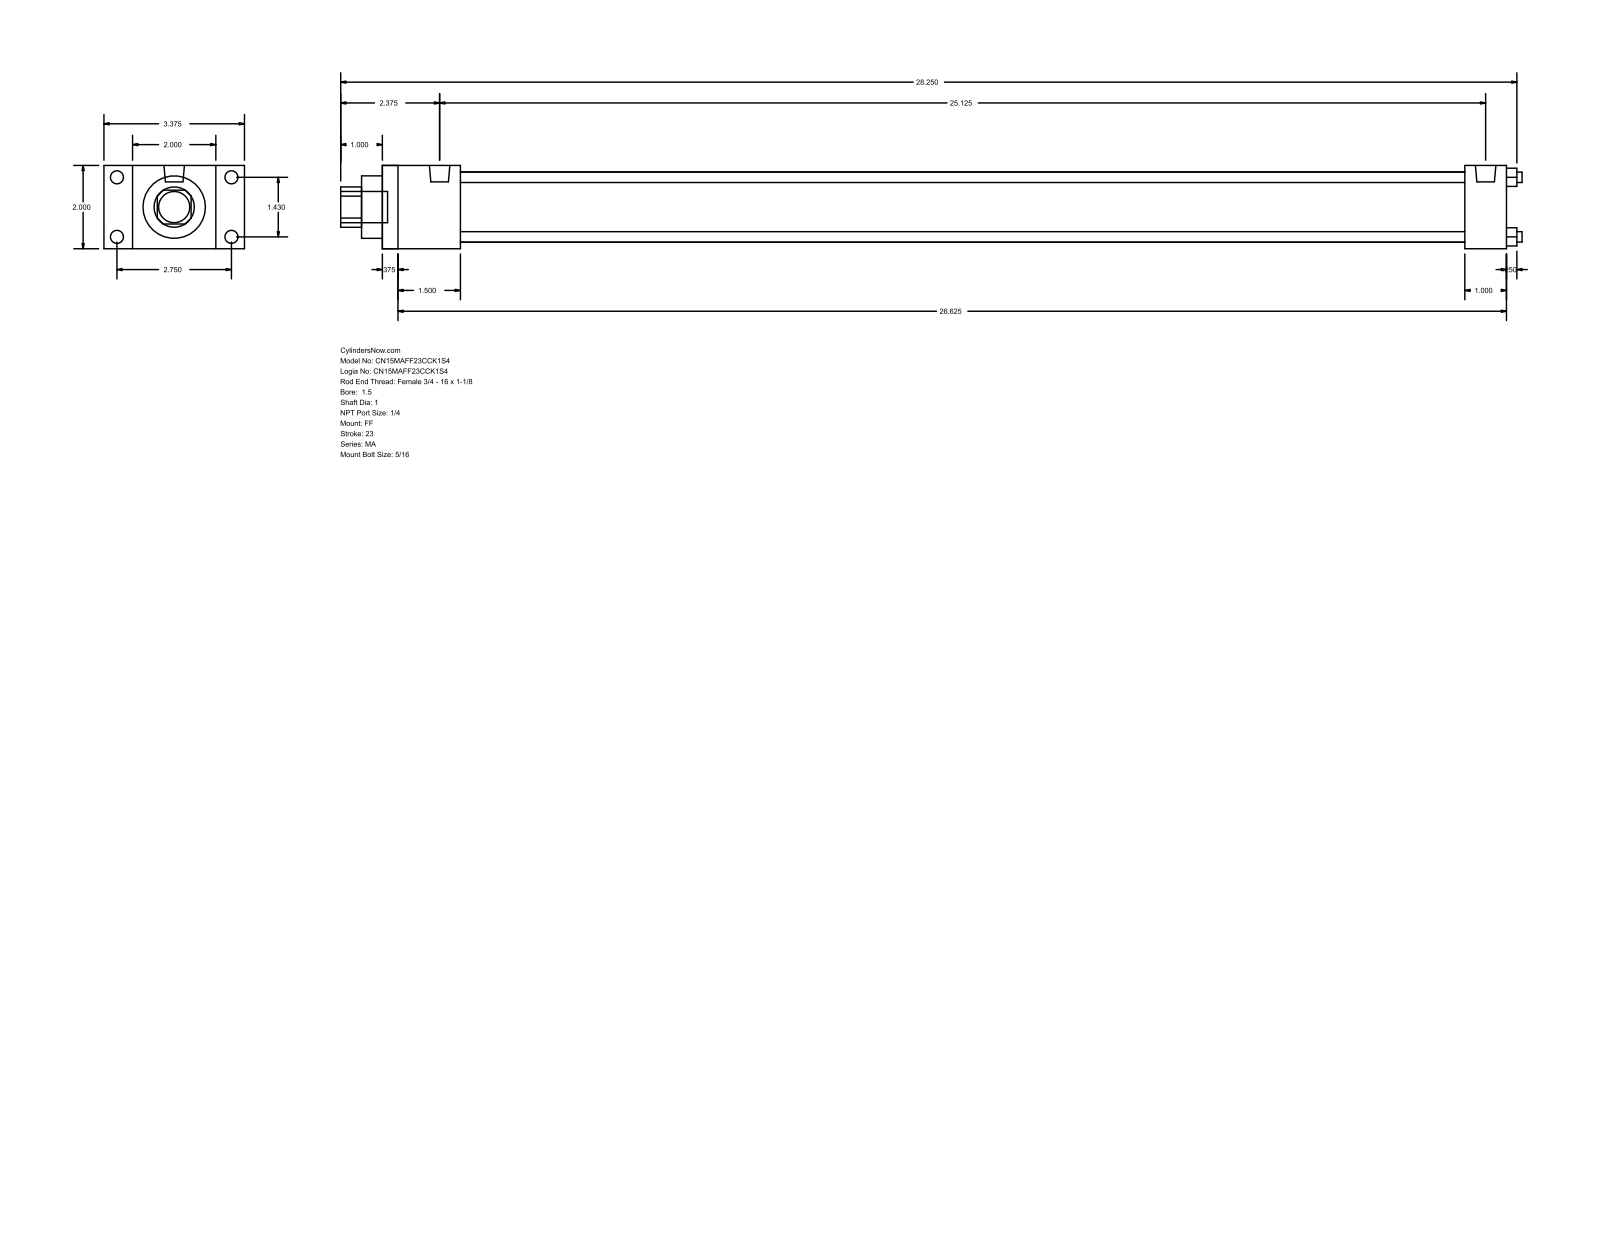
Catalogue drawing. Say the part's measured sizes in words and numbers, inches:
The part is named "MA_FF__0150_1". Its 3-D file was written by "GSSL Pune (CONFIG_CONTROL_DESIGN)". It is 0 solids with 92 faces: 64 planar, 28 cylindrical and 0 other. Overall it measures 28.375 by 3.375 by 2 inches. Round holes: 4 of diameter 0.25, 1 of diameter 1, 1 of diameter 1.5, 1 of diameter 1.69. Round bosses or shafts: 8 of diameter 0.313, 2 of diameter 0.492, 1 of diameter 0.75. Partial cylindrical surfaces (rounded edges, fillets, slot ends): 1 of radius 0.484. The main face-to-face distances are 2, 27, 0.375, 26.625, 1, 1.875, 26, 1.5, 25.625, 24.125. The hole center spacings are 1.011, 1.43, 2.022.
